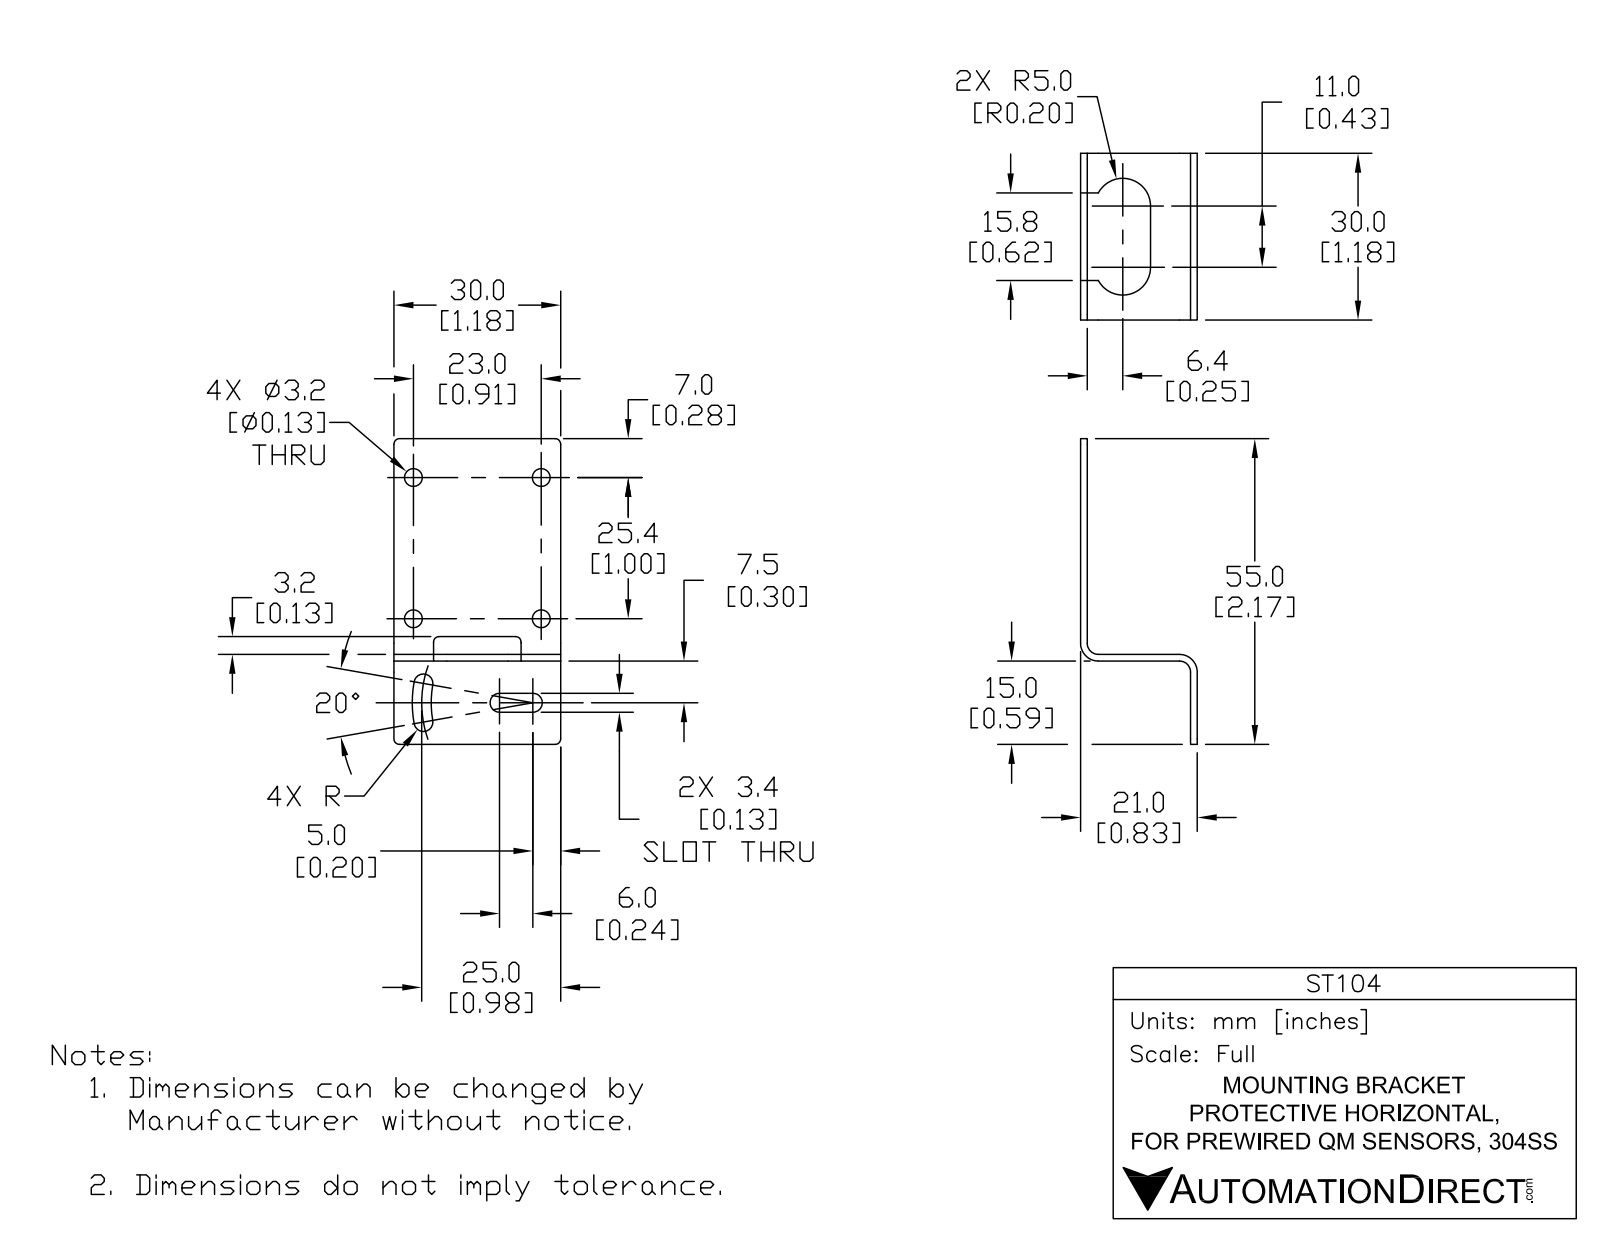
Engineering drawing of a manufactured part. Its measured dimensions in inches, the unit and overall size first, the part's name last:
Units: inches
Overall size (bounding box): 2.165 × 1.181 × 0.827
Round holes (diameter × count): ⌀0.126 ×4
Partial cylindrical surfaces — rounded edges, fillets, slot ends (radius × count): R0.039 ×6, R0.067 ×4, R0.079 ×2, R0.126 ×2, R0.197 ×2, R0.72 ×1, R0.854 ×1
Main face-to-face distances: 0.047, 0.78, 0.827, 0.732, 1.181, 0.591, 0.638, 2.165, 1.575, 1.528
Hole centre spacings: 0.906, 1, 1.349
Volume: 0.133 in³ · Surface area: 6.297 in²
Bodies: 1 solid, 45 faces (16 planar, 29 cylindrical, 0 other)
Part name (STEP PRODUCT): ST104
STEP written by: SolidWorks 2017 (AUTOMOTIVE_DESIGN)
